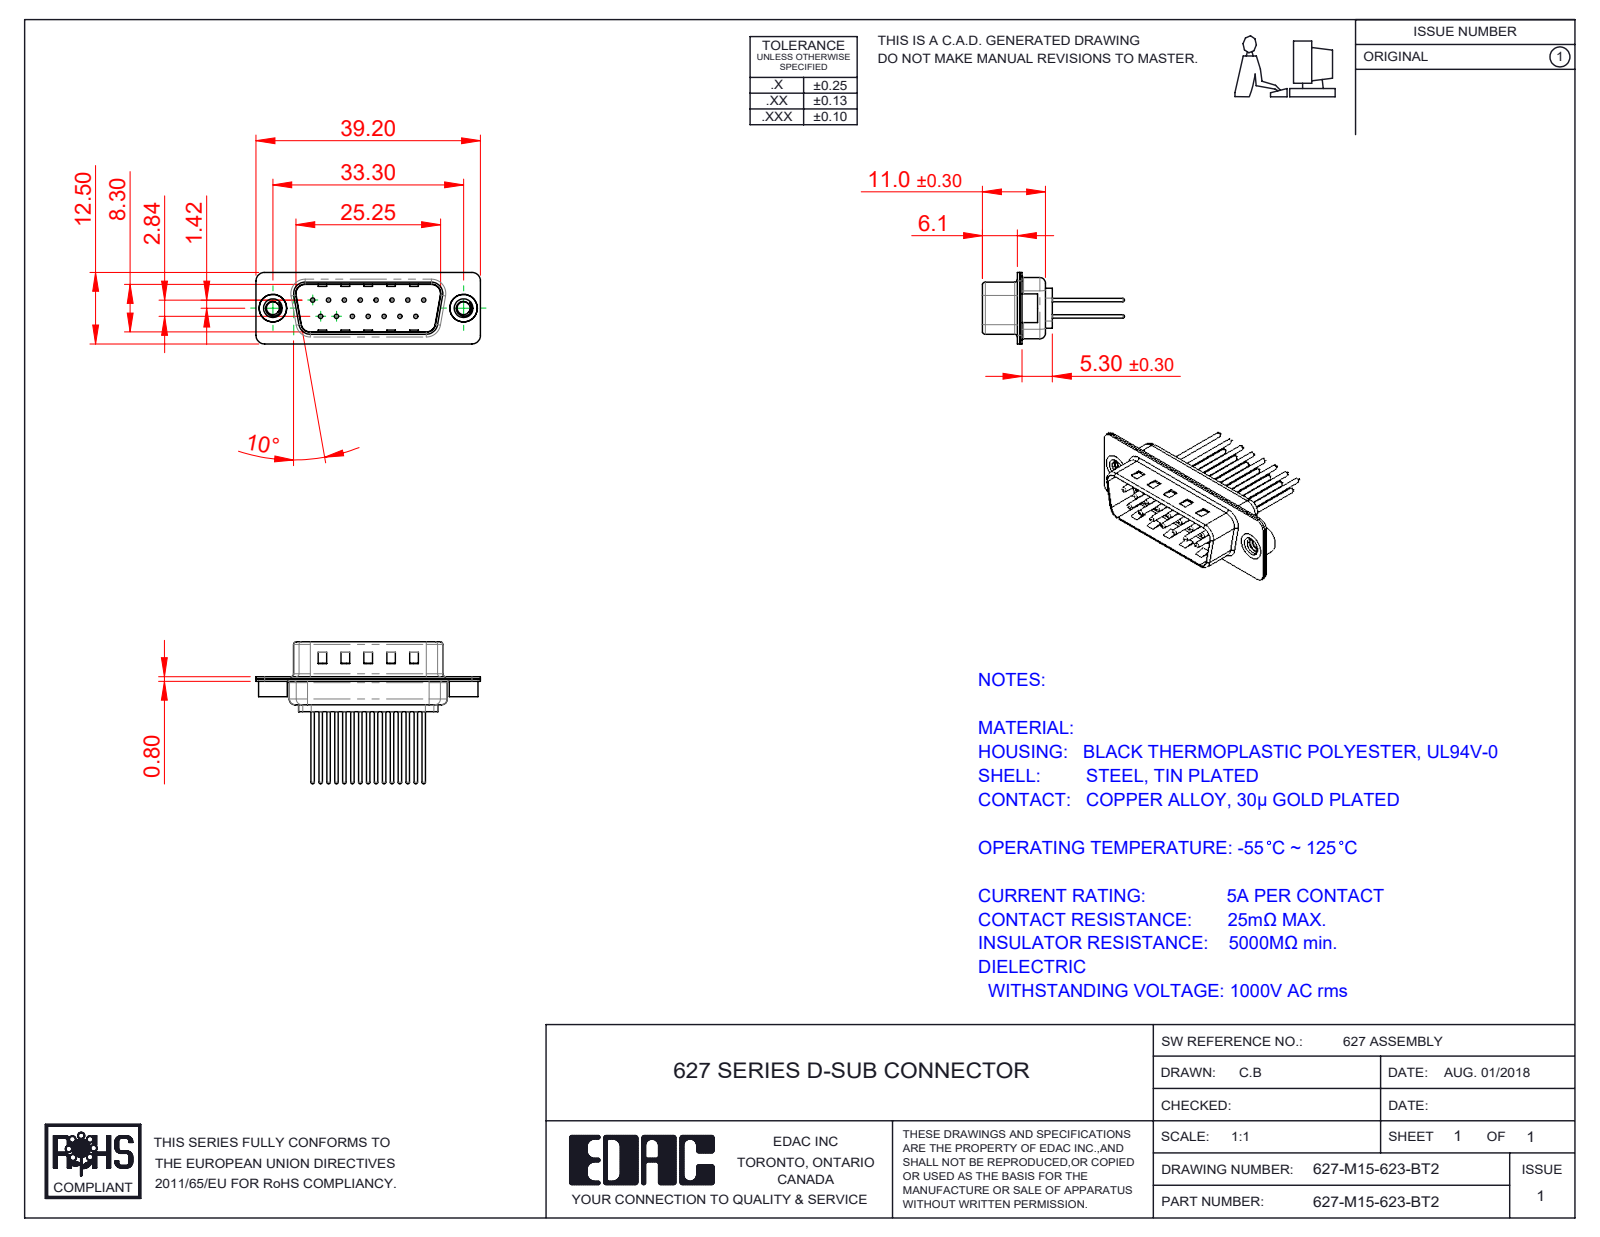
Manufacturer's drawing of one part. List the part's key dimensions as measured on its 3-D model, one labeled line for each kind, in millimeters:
Part name (STEP PRODUCT): 627M 4-40 Threaded Rivet; 627M Housing_15 Contacts; 627M Shell Front_15 Contacts; 627-M15-623-BT2 (+3 more)
STEP written by: SolidWorks 2020 (CONFIG_CONTROL_DESIGN)
Units: millimetres
Bodies: 20 solids, 895 faces (244 planar, 343 cylindrical, 308 other)
Overall size (bounding box): 39.2 × 24.77 × 12.5
Volume: 1 873 mm³ · Surface area: 5 003 mm²
Round holes (diameter × count): ⌀0.75 ×15, ⌀1.6 ×15, ⌀2 ×15, ⌀2.26 ×2, ⌀4 ×2, ⌀4.8 ×2
Round bosses / shafts (diameter × count): ⌀1.5 ×15, ⌀0.6 ×15, ⌀5 ×2, ⌀4.9 ×2
Partial cylindrical surfaces — rounded edges, fillets, slot ends (radius × count): R1.5 ×16, R2 ×12, R0.5 ×8, R1.6 ×8, R0.25 ×4, R0.6 ×4, R0.65 ×4, R0.9 ×4
Main face-to-face distances: 0.4, 0.8, 9.5, 9.1, 8.7, 9.9, 1.2, 6.1, 5.3, 5.7
Hole centre spacings: 3.16, 2.77, 5.54, 8.31, 11.08, 5.03, 5.04, 7.48
